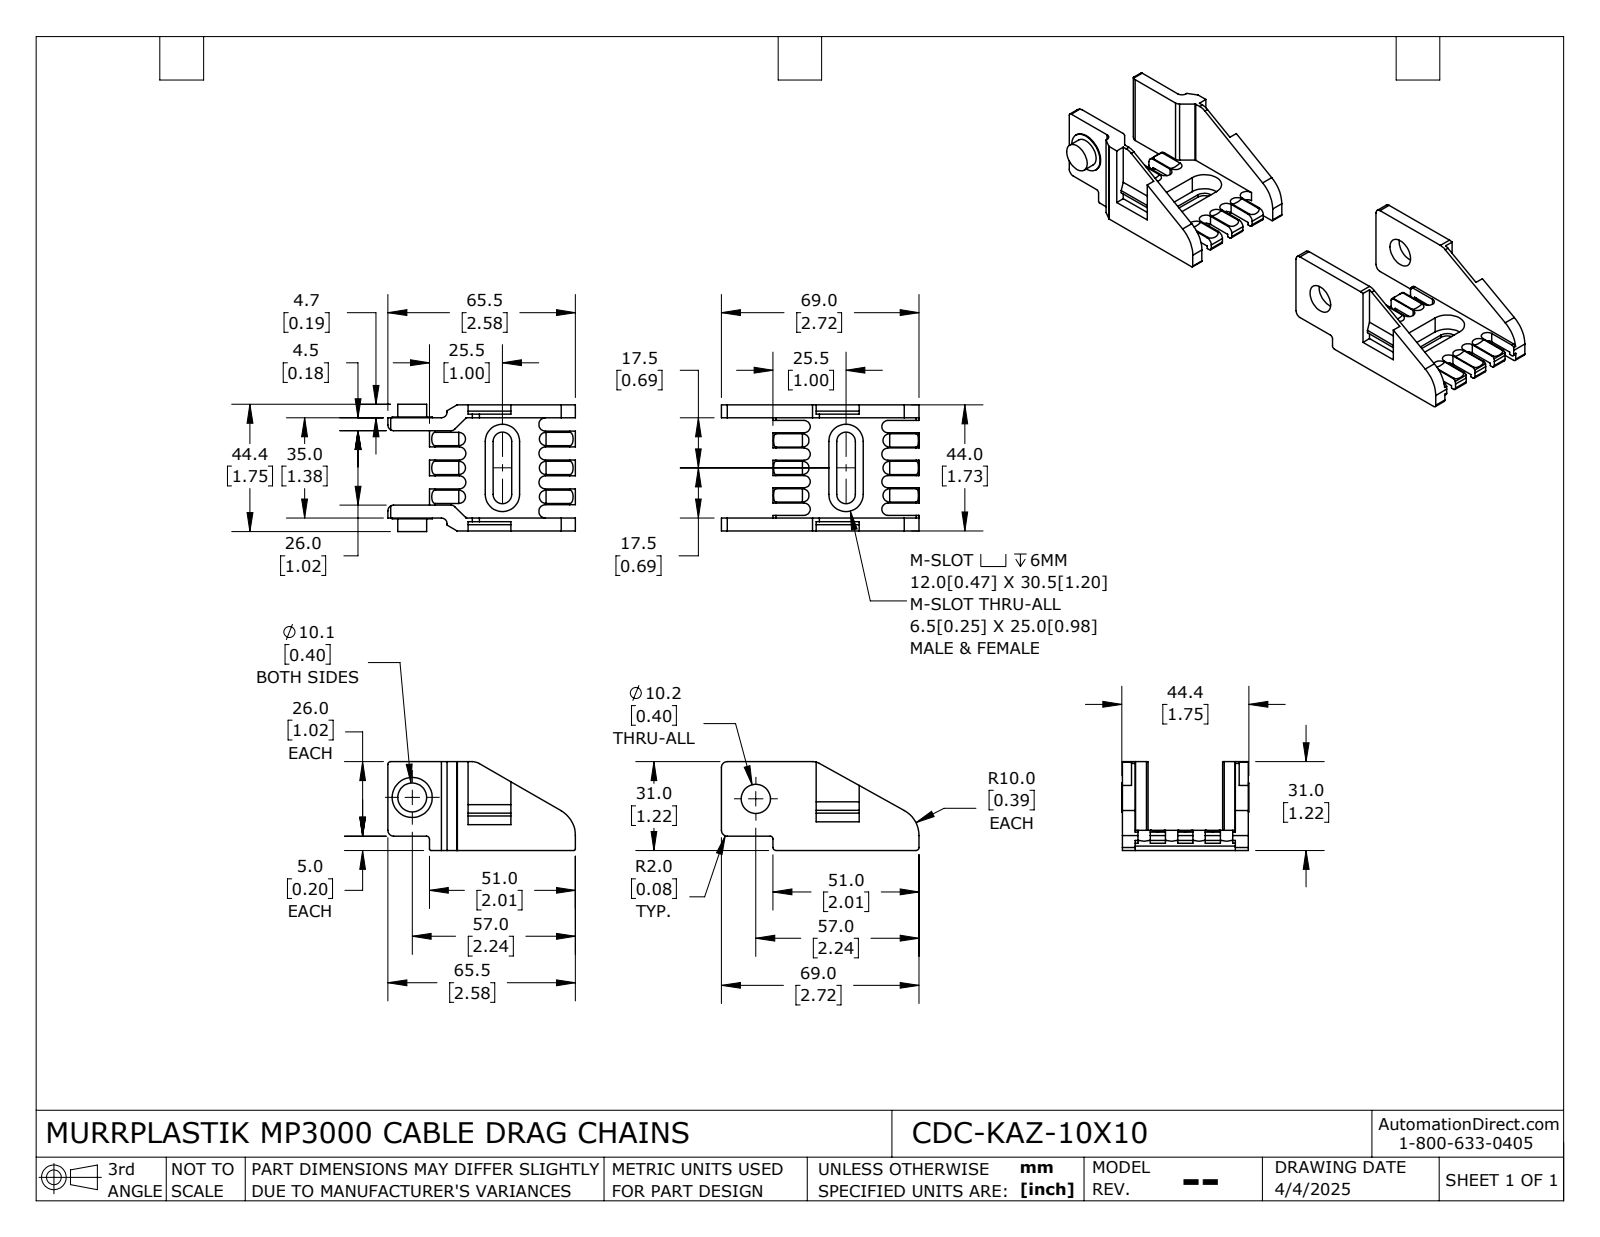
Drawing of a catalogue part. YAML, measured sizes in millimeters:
part_name: "CDC-KAZ-10X10"
step_written_by: "SolidWorks 2024 (AUTOMOTIVE_DESIGN)"
units: millimeters
bodies: {solids: 2, faces: 327, planar: 190, cylindrical: 125, other: 12}
overall_size: [185.5, 44.4, 31]
volume: 38315
surface_area: 24226
round_holes:
  - {diameter: 10.2, count: 1}
round_bosses_or_shafts:
  - {diameter: 14, count: 1}
  - {diameter: 10.1, count: 1}
partial_cylinders:
  - {radius: 2, count: 13}
  - {radius: 1, count: 11}
  - {radius: 2.15, count: 8}
  - {radius: 7, count: 6}
  - {radius: 0.5, count: 4}
  - {radius: 2.3, count: 4}
  - {radius: 3.25, count: 4}
  - {radius: 6, count: 4}
face_to_face_distances: [4.5, 39.5, 35, 44, 7, 3.5, 9, 30.5, 3.2, 40.8]
